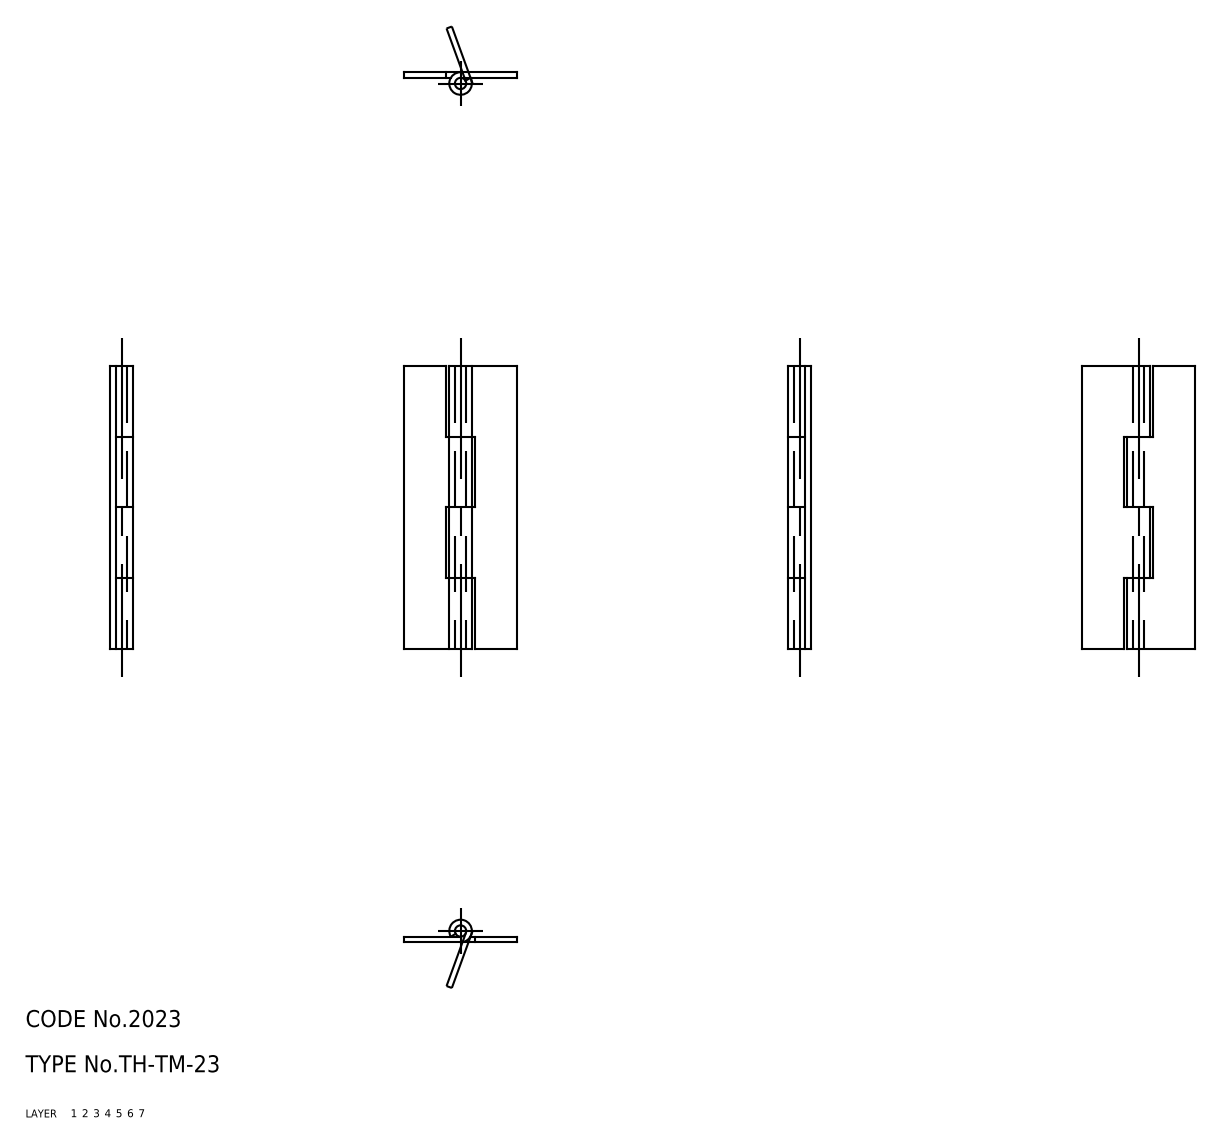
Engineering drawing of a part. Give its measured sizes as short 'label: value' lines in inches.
name: hinge piece_B; hinge piece_A; shaft; TH_TM_23_22101_36
written by: CADfix (AUTOMOTIVE_DESIGN)
unit: in
bodies: 3 solids, 36 faces (0 planar, 0 cylindrical, 36 other)
size: 1.969 × 0.787 × 0.157
volume: 0.087 in³; area: 4.906 in²
